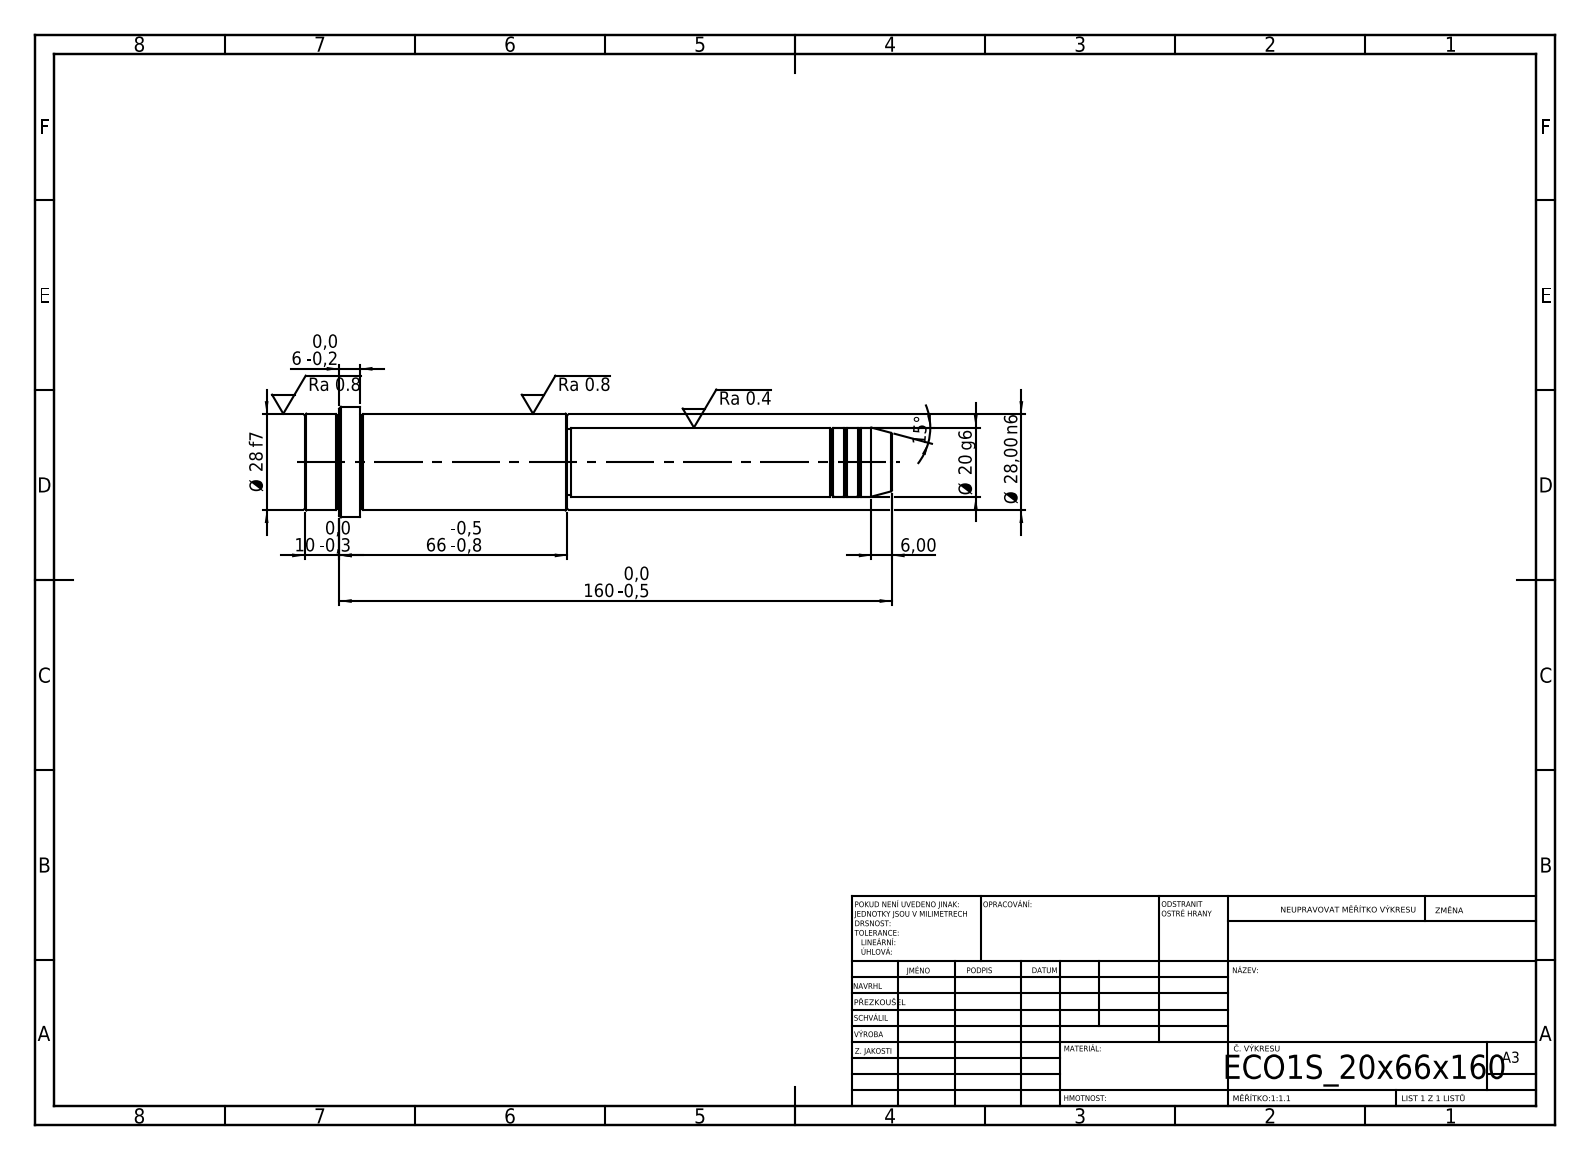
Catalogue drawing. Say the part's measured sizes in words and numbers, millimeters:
Its 3-D file was written by "SolidWorks 2019 (CONFIG_CONTROL_DESIGN)". It is 1 solid with 52 faces: 6 planar, 16 cylindrical and 30 other. Overall it measures 170 by 32 by 32 millimeters. Its volume is 76 966 cubic millimeters and its surface area 14 327 square millimeters. Round bosses or shafts: 1 of diameter 32, 1 of diameter 28, 1 of diameter 20, 1 of diameter 19. The main face-to-face distances are 76, 94, 170, 154, 60, 16, 160, 66, 6, 10.
